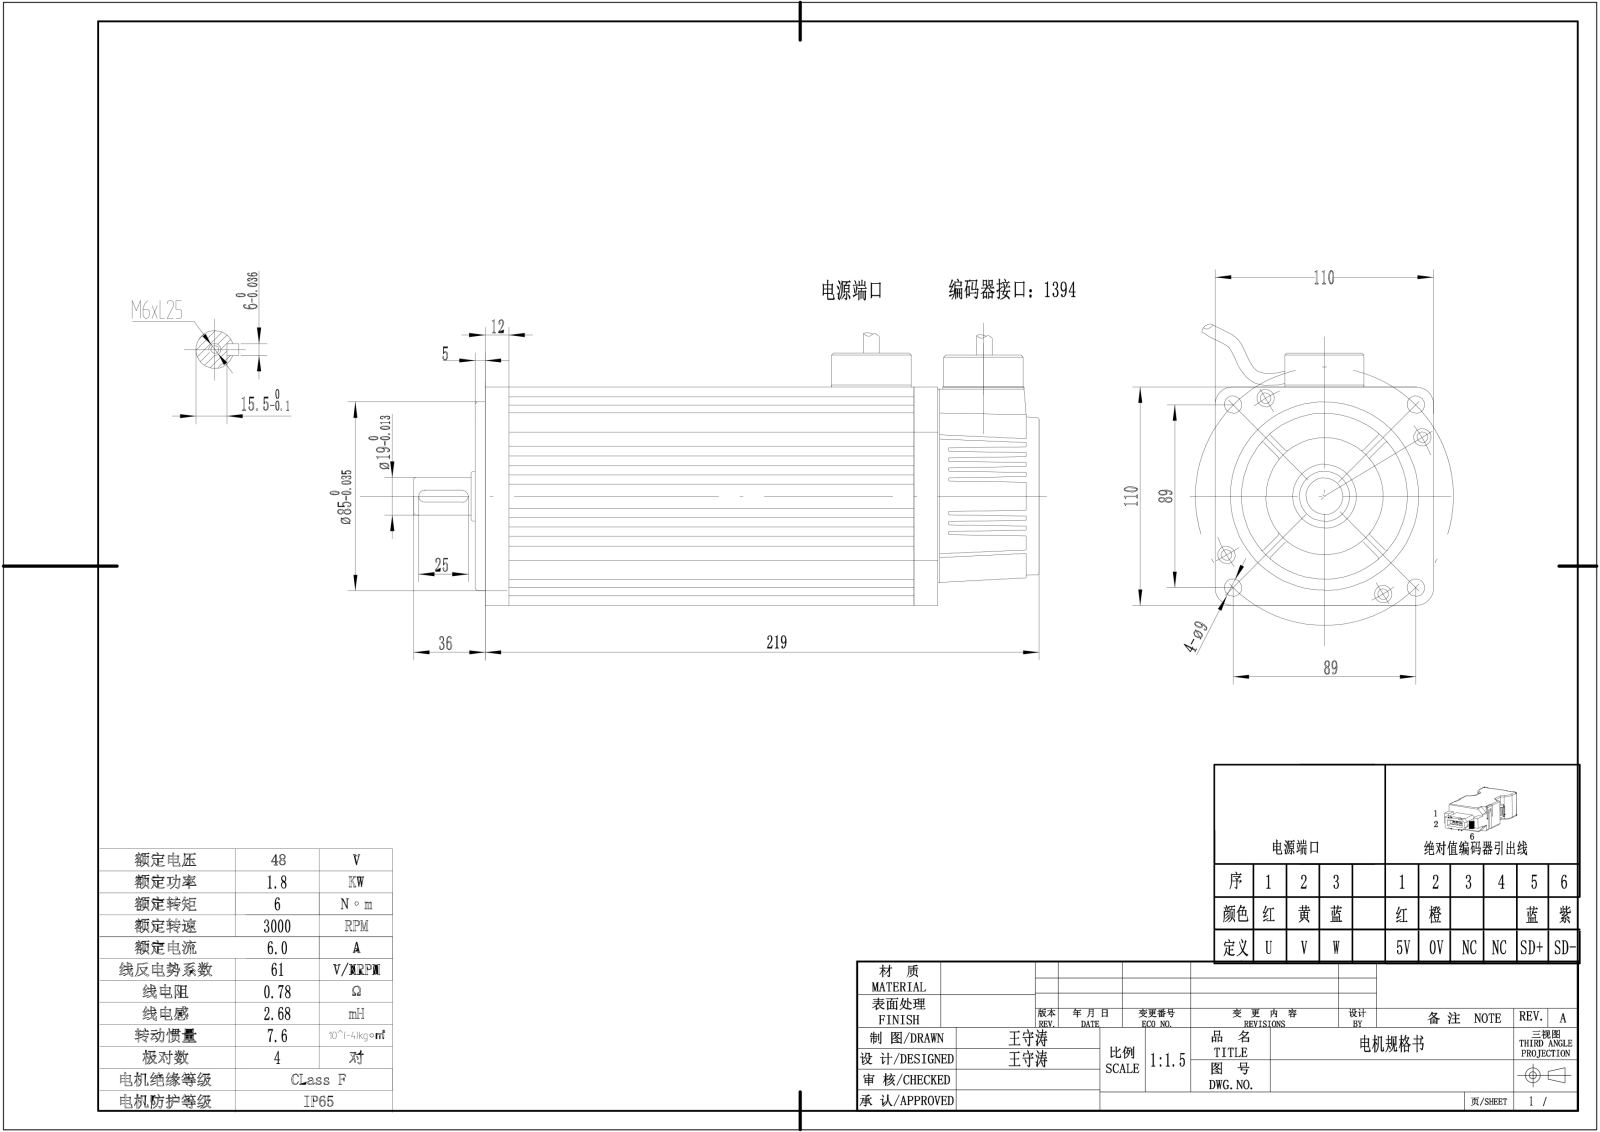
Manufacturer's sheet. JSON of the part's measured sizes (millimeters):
{"part_name": ".STEP; 110_____2-0.STEP; 110 ________.STEP; M110SFM-C06030-XXB1 (+8 more)", "step_written_by": "SolidWorks 2020 (AUTOMOTIVE_DESIGN)", "units": "millimeters", "bodies": {"solids": 9, "faces": 731, "planar": 492, "cylindrical": 203, "other": 36}, "overall_size": [274, 155, 110], "volume_mm3": 1112000, "surface_area_mm2": 340871, "round_holes": [[2.5, 16], [5.5, 12], [10, 12], [9, 4], [25, 2], [5, 1], [20, 1], [26, 1], [30, 1], [39, 1], [40, 1], [46, 1]], "round_bosses_or_shafts": [[1.5, 15], [5, 3], [102, 1], [95, 1], [74, 1], [70, 1], [65, 1], [60, 1]], "partial_cylinders_radius": [[5, 4], [3, 2]], "face_to_face_distances": [17, 5, 110, 12, 2.26, 157, 5.1, 64.42, 93, 7], "hole_center_spacings": [10.27, 14.72, 20.58, 22.48, 44.73, 55, 57.32, 63.26]}
